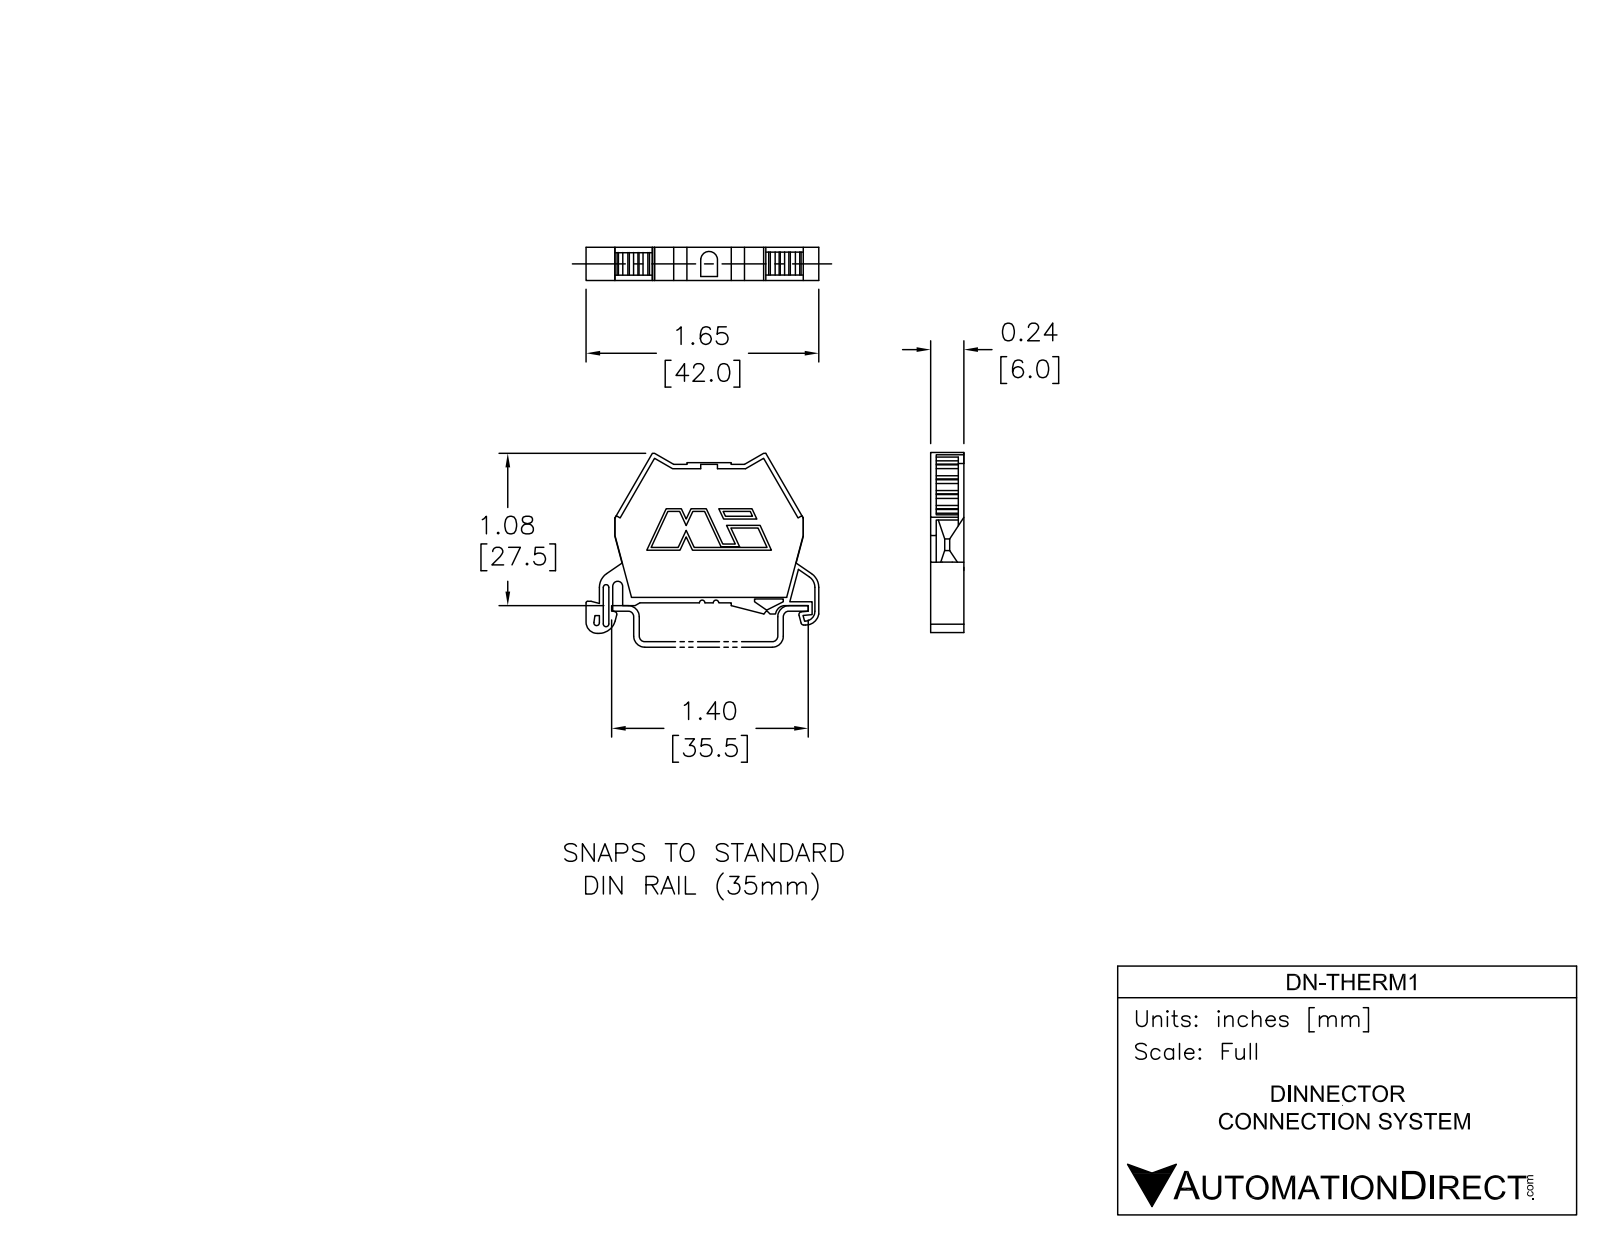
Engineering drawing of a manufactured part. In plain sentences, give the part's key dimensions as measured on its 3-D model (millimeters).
The part is named "DN-THERM1". Its 3-D file was written by "SolidWorks 2021 (CONFIG_CONTROL_DESIGN)". It is 1 solid with 170 faces: 141 planar, 29 cylindrical and 0 other. Overall it measures 42 by 32.5 by 6.25 millimeters. Its volume is 4 604 cubic millimeters and its surface area 3 444 square millimeters. Partial cylindrical surfaces (rounded edges, fillets, slot ends): 8 of radius 0.5, 3 of radius 3, 1 of radius 0.3, 1 of radius 0.9, 1 of radius 1.62, 1 of radius 1.7, 1 of radius 1.8, 1 of radius 2. The main face-to-face distances are 6, 0.7, 1, 5, 3.25, 1.7, 1.5, 37.2, 1.19, 2.62.
